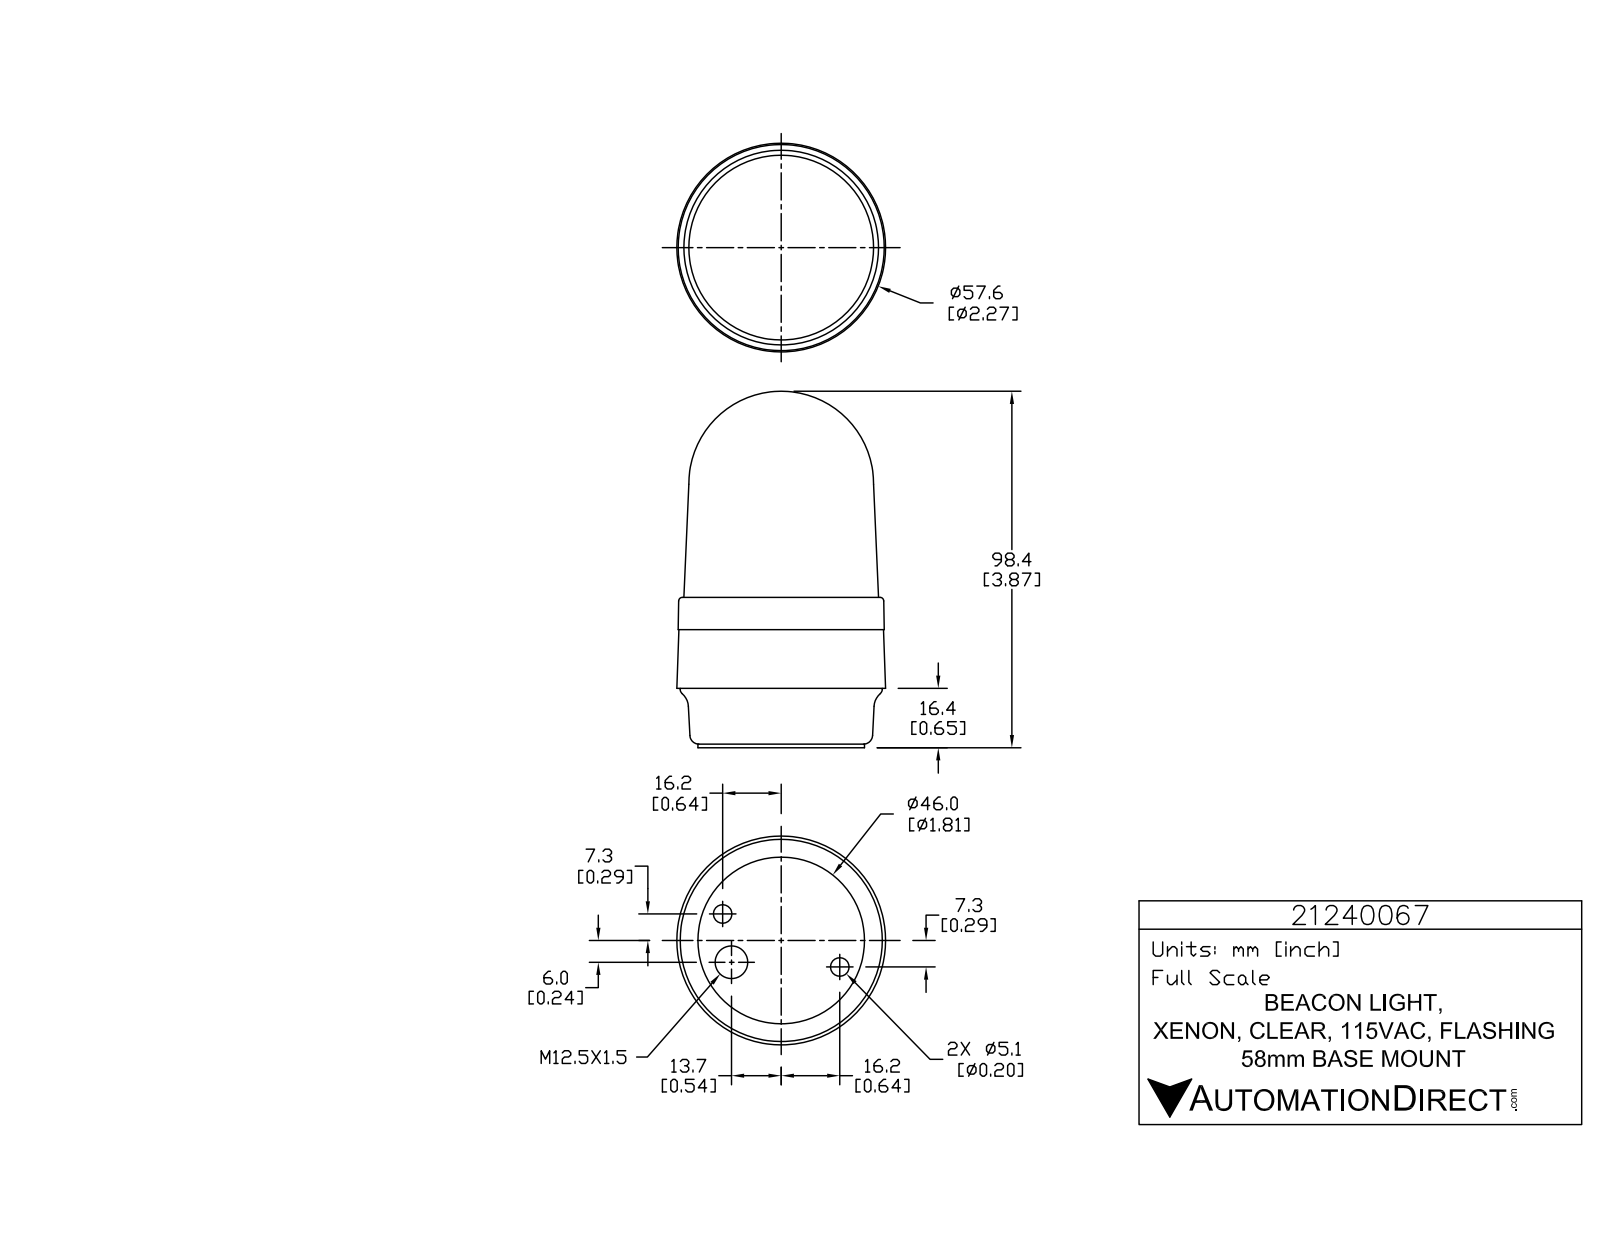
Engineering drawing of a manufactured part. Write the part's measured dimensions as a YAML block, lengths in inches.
part_name: "21240067"
step_written_by: "SolidWorks 2015 (AUTOMOTIVE_DESIGN)"
units: inches
bodies: {solids: 1, faces: 764, planar: 527, cylindrical: 145, other: 92}
overall_size: [3.874, 2.269, 2.269]
volume: 12.2
surface_area: 29.33
round_holes:
  - {diameter: 0.039, count: 3}
  - {diameter: 0.201, count: 2}
  - {diameter: 0.354, count: 1}
round_bosses_or_shafts:
  - {diameter: 0.226, count: 3}
  - {diameter: 0.056, count: 3}
  - {diameter: 2.197, count: 1}
  - {diameter: 1.811, count: 1}
partial_cylinders:
  - {radius: 0.008, count: 6}
  - {radius: 0.008, count: 6}
  - {radius: 0.008, count: 6}
  - {radius: 0.131, count: 6}
  - {radius: 0.004, count: 3}
  - {radius: 0.005, count: 3}
  - {radius: 0.007, count: 3}
  - {radius: 0.008, count: 3}
face_to_face_distances: [0.646, 0.039, 0.606, 1.634, 1.594, 0.988, 1.283, 1.244, 0.638, 0.35]
hole_center_spacings: [0.534, 1.179, 1.398]
